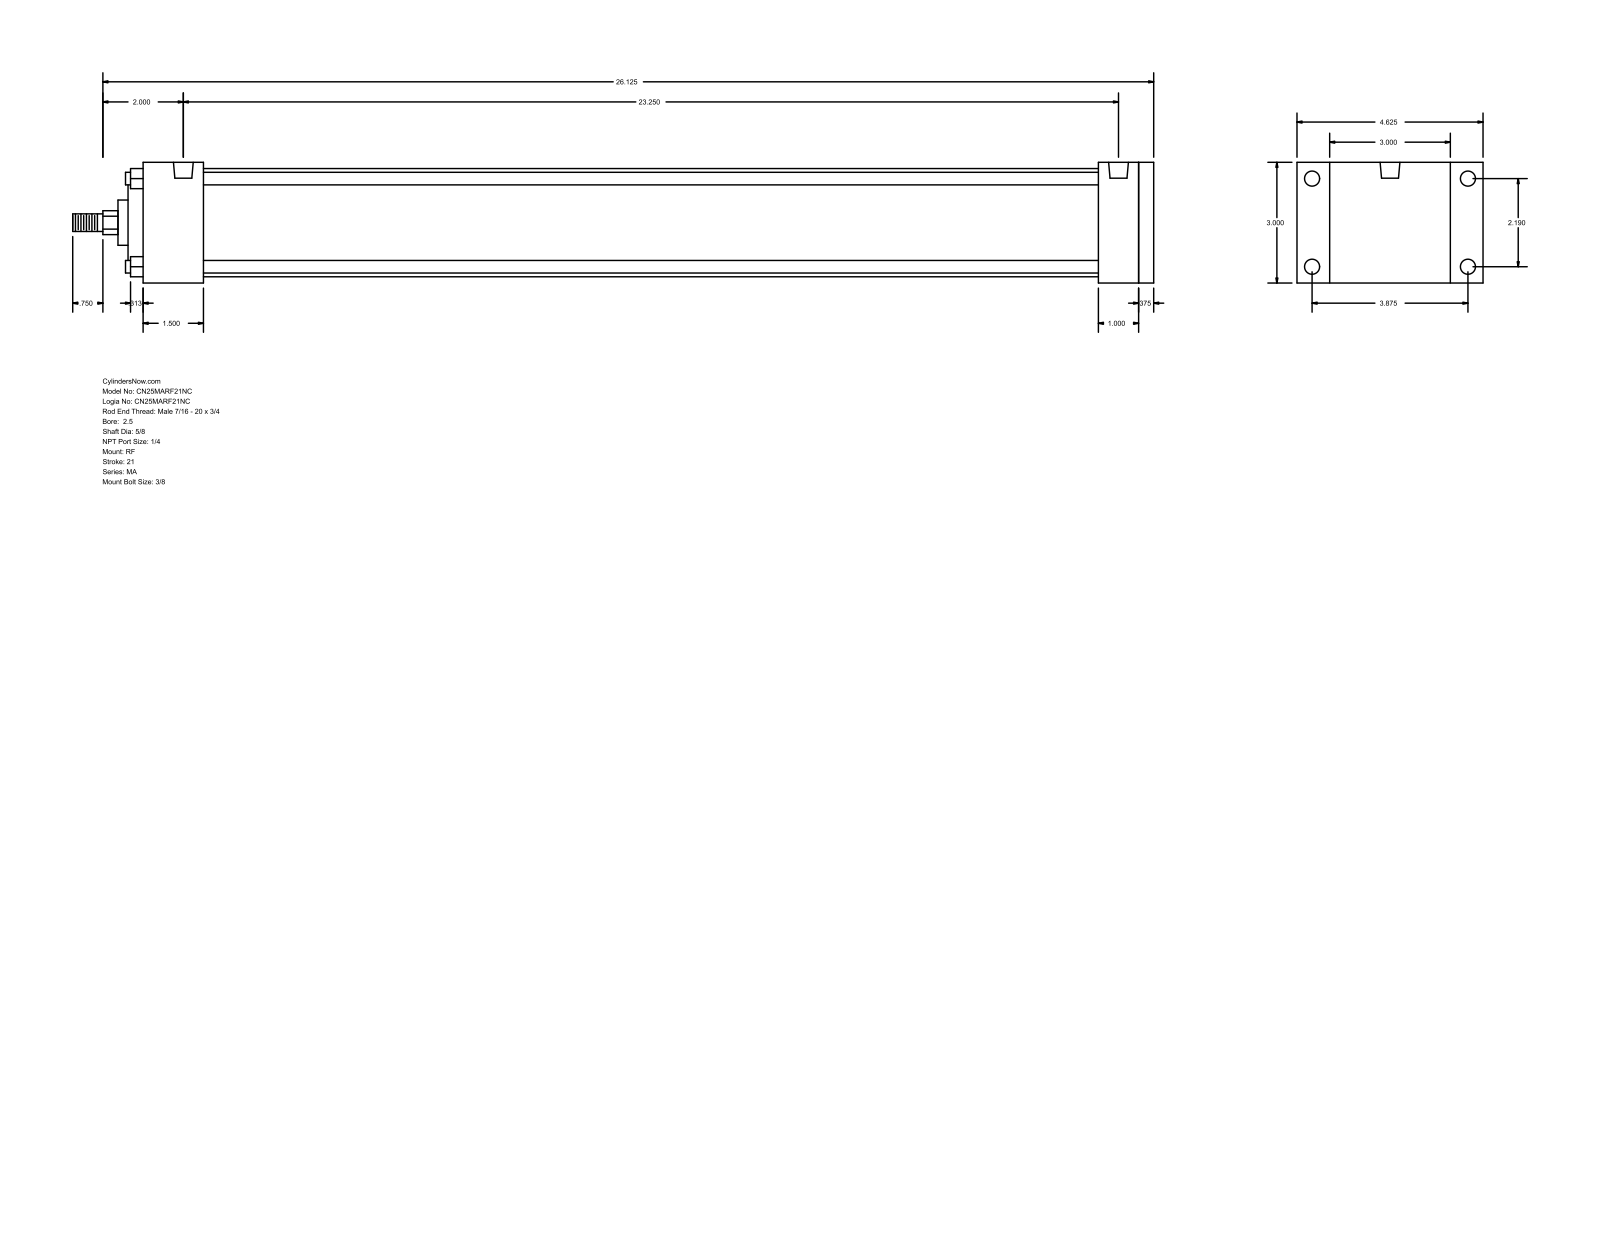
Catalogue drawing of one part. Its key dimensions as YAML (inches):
part_name: "MA_RF__0250_0.625"
step_written_by: "GSSL Pune (CONFIG_CONTROL_DESIGN)"
units: inches
bodies: {solids: 0, faces: 94, planar: 65, cylindrical: 29, other: 0}
overall_size: [26.875, 4.625, 3]
round_holes:
  - {diameter: 0.313, count: 4}
  - {diameter: 0.375, count: 4}
  - {diameter: 0.492, count: 2}
round_bosses_or_shafts:
  - {diameter: 0.313, count: 4}
  - {diameter: 2.69, count: 1}
  - {diameter: 2, count: 1}
  - {diameter: 1.125, count: 1}
  - {diameter: 0.625, count: 1}
  - {diameter: 0.437, count: 1}
partial_cylinders:
  - {radius: 0.297, count: 1}
face_to_face_distances: [3, 25.125, 0.375, 24.75, 1, 1.375, 1.5, 23.75, 22.25, 23.25]
hole_center_spacings: [2.19, 3.875, 4.451, 23.25]
